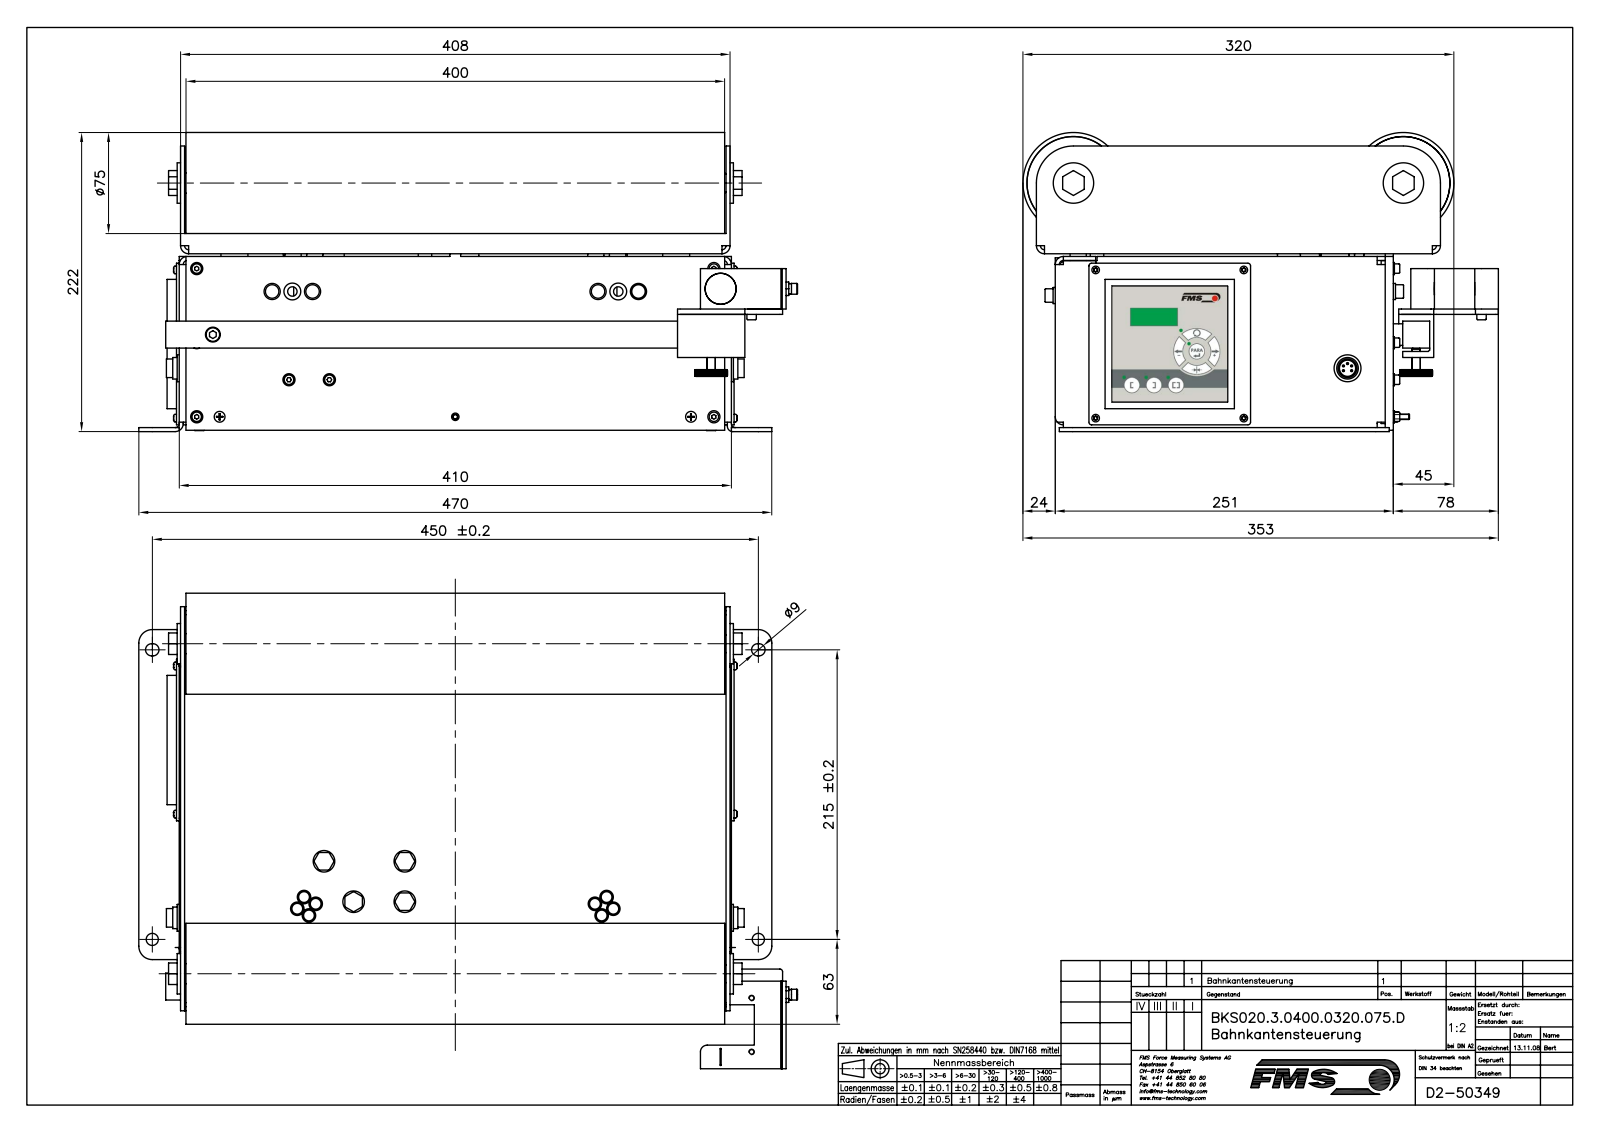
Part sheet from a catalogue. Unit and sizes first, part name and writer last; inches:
Units: inches
Overall size (bounding box): 19.256 × 13.898 × 8.74
Round holes (diameter × count): ⌀0.118 ×30, ⌀0.126 ×14, ⌀0.169 ×14, ⌀0.135 ×13, ⌀0.102 ×12, ⌀0.252 ×12, ⌀0.087 ×8, ⌀0.209 ×8, ⌀0.138 ×7, ⌀0.236 ×6, ⌀0.331 ×6, ⌀0.039 ×4
Round bosses / shafts (diameter × count): ⌀0.394 ×22, ⌀0.157 ×18, ⌀0.315 ×15, ⌀0.236 ×15, ⌀0.472 ×12, ⌀0.276 ×10, ⌀0.354 ×8, ⌀0.197 ×8
Partial cylindrical surfaces — rounded edges, fillets, slot ends (radius × count): R0.013 ×48, R0.039 ×29, R0.079 ×25, R0.01 ×24, R0.022 ×24, R0.008 ×20, R0.01 ×19, R0.118 ×14
Main face-to-face distances: 0.118, 0.039, 5, 0.079, 5.118, 0.197, 5.039, 5.157, 0.157, 0.236
Hole centre spacings: 0.394, 3.287, 3.836, 3.853, 4.331, 8.506, 3.268, 0.028
Volume: 186.4 in³ · Surface area: 2 796 in²
Bodies: 172 solids, 6045 faces (3692 planar, 1877 cylindrical, 476 other)
Part name (STEP PRODUCT): K50349; K0601245; K0601244; TEIL1 (+8 more)
STEP written by: Mechanical Desktop 2007 (CONFIG_CONTROL_DESIGN)
